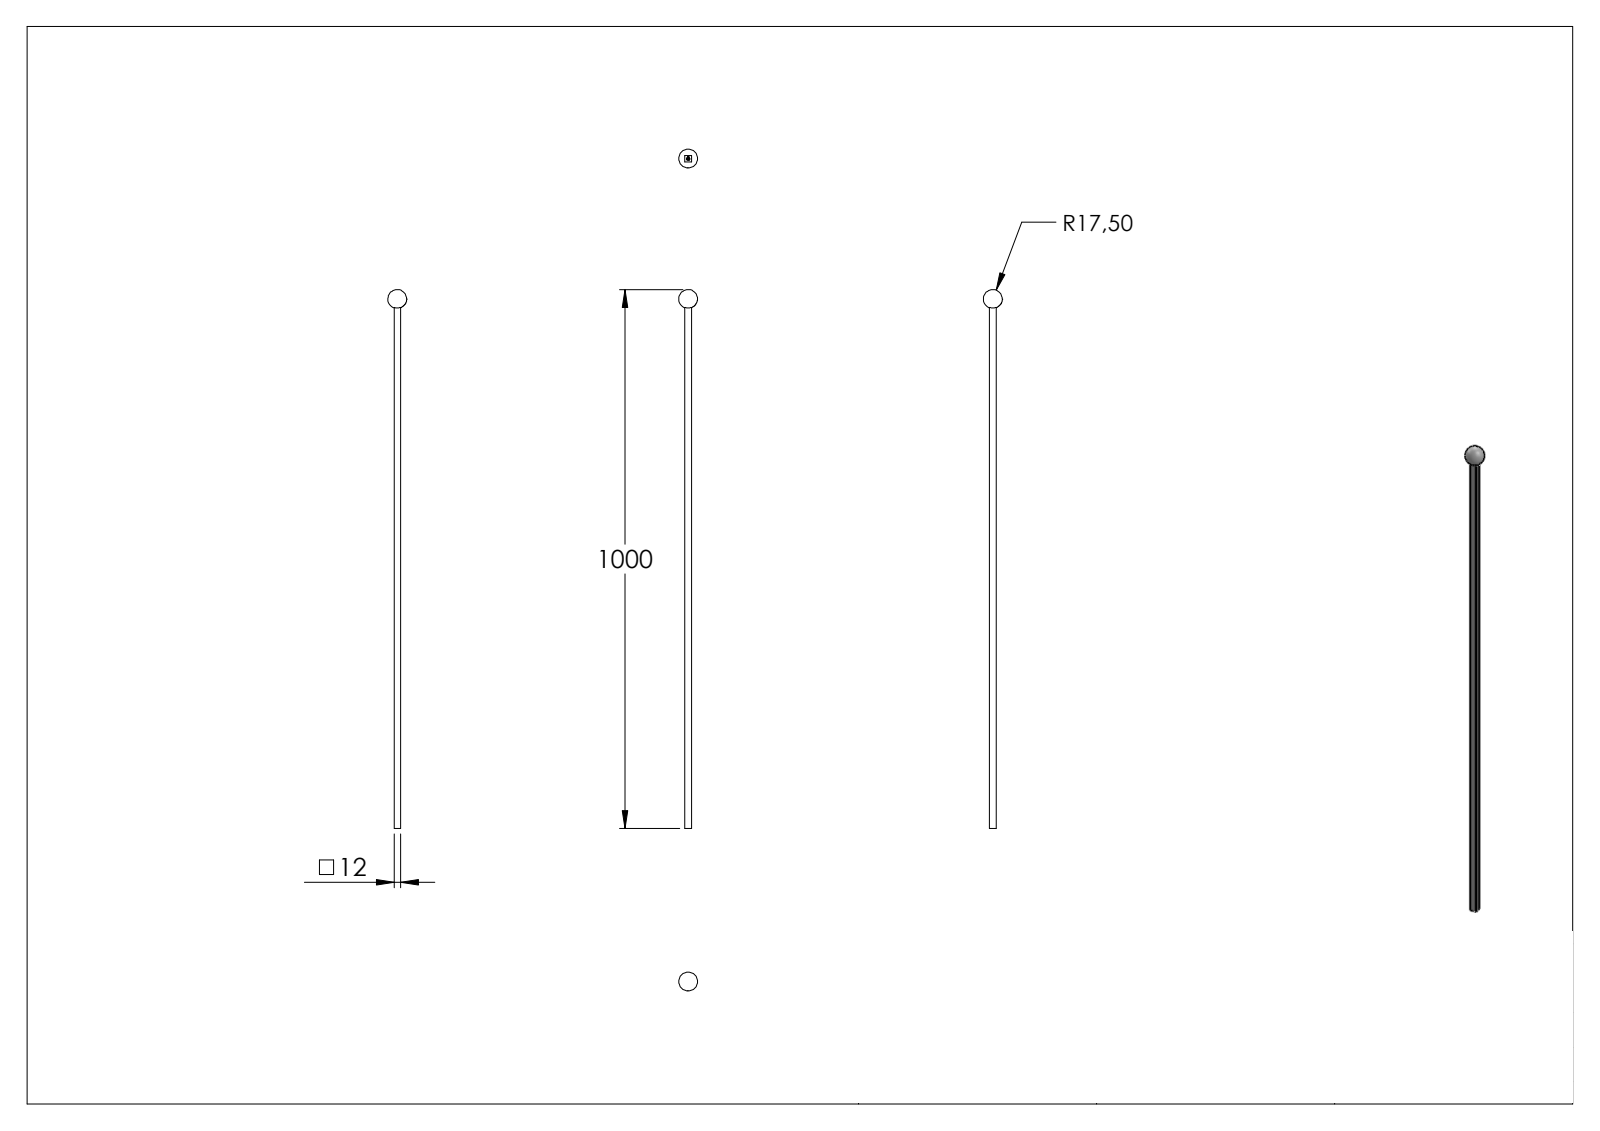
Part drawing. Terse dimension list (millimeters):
name: 1307-IT-35
written by: SolidWorks 2018 (CONFIG_CONTROL_DESIGN)
unit: mm
bodies: 1 solid, 262 faces (148 planar, 0 cylindrical, 114 other)
size: 1000 × 35 × 35
volume: 161 511 mm³; area: 50 239 mm²
face distances: 12, 0.36, 1.76, 2.32, 5, 7, 1.21, 1.71, 0.92, 0.54
